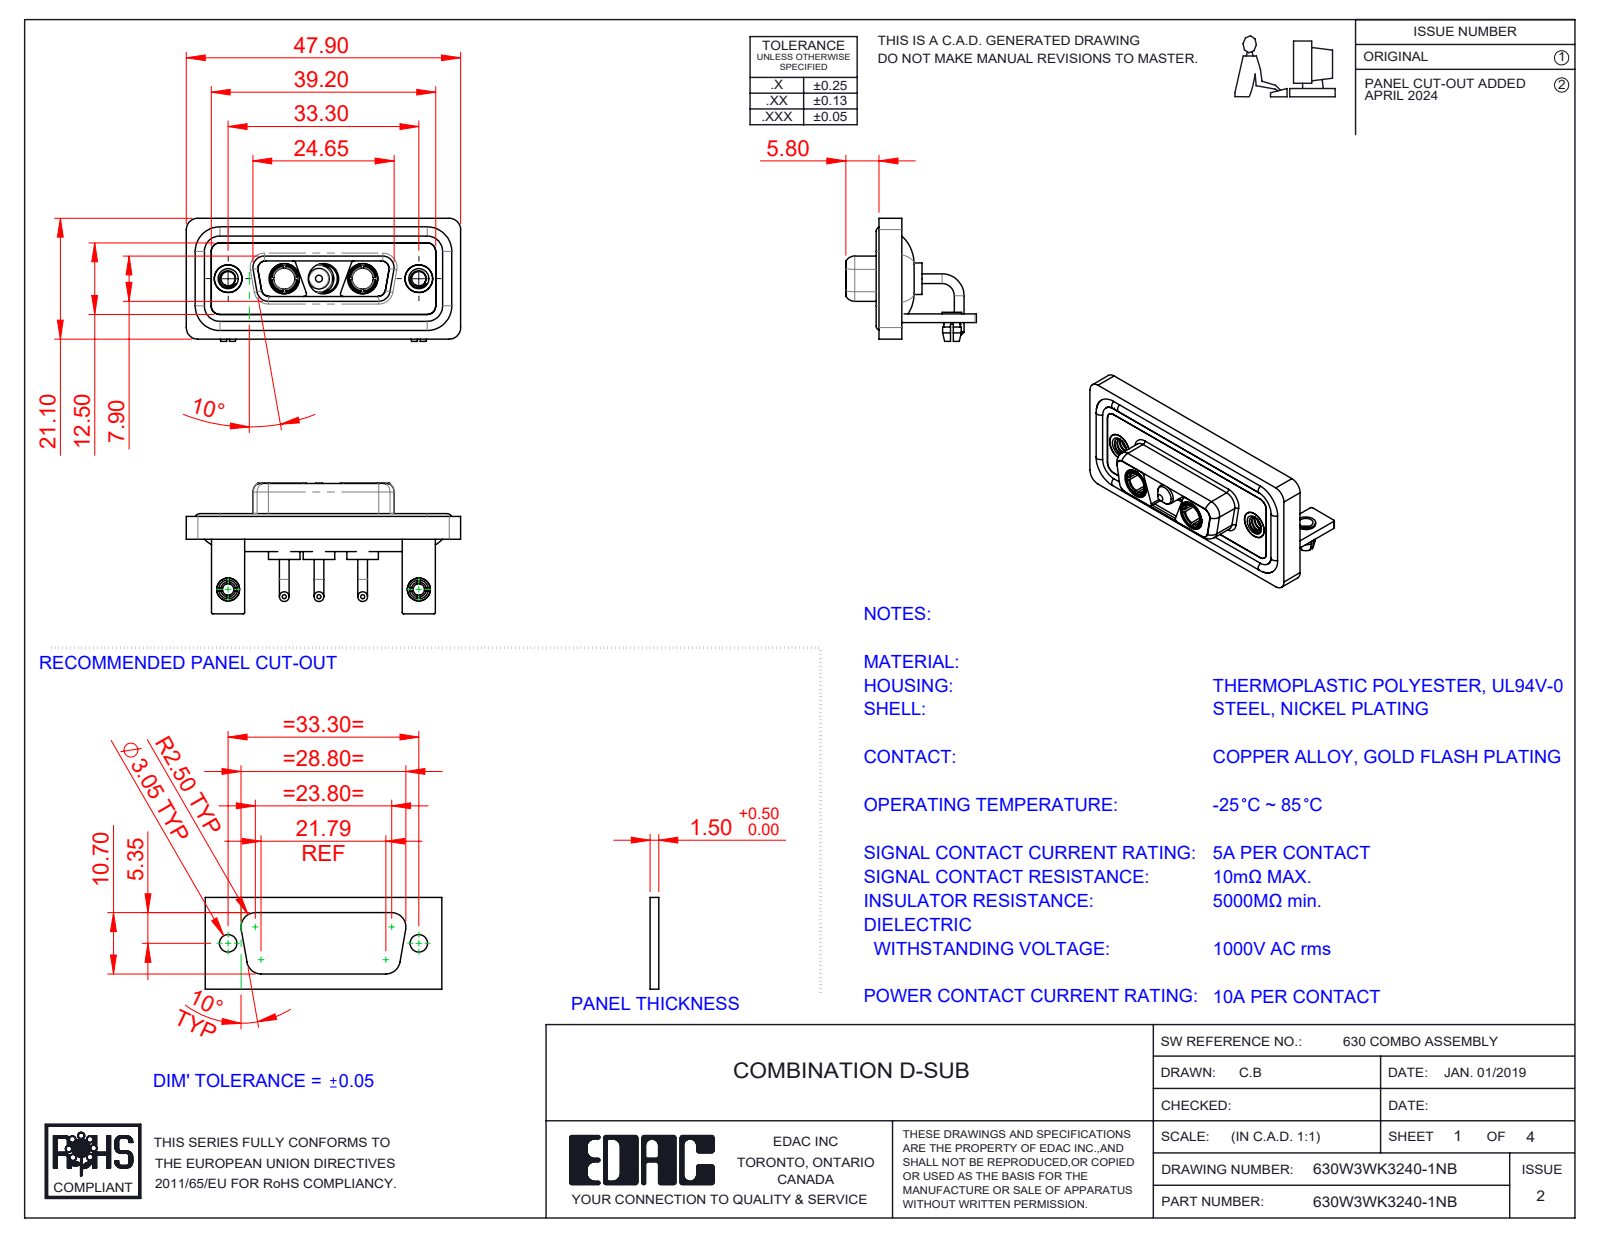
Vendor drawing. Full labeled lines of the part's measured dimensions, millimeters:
Part name (STEP PRODUCT): Power Socket_10A RA; 630Combo Shell Rear_15 Contacts; 630Combo Board Lock_50 Contacts; Power Pin_10A RA (+6 more)
STEP written by: SolidWorks 2023 (CONFIG_CONTROL_DESIGN)
Units: millimetres
Bodies: 17 solids, 729 faces (246 planar, 318 cylindrical, 165 other)
Overall size (bounding box): 47.9 × 22.8 × 21.5
Volume: 6 254 mm³ · Surface area: 10 535 mm²
Round holes (diameter × count): ⌀4.85 ×5, ⌀2.5 ×4, ⌀5.3 ×3, ⌀2 ×2, ⌀3.2 ×2, ⌀3.7 ×2, ⌀4 ×2, ⌀4.05 ×2, ⌀5 ×2
Round bosses / shafts (diameter × count): ⌀1.7 ×6, ⌀1.6 ×4, ⌀5.5 ×3, ⌀5.2 ×3, ⌀4.75 ×3, ⌀3.75 ×3, ⌀4.96 ×2, ⌀4.95 ×2
Partial cylindrical surfaces — rounded edges, fillets, slot ends (radius × count): R2 ×21, R1.5 ×18, R0.25 ×16, R1.35 ×12, R0.5 ×9, R1.6 ×8, R0.6 ×4, R0.65 ×4
Main face-to-face distances: 0.4, 2.9, 1.5, 3.7, 1.8, 1.1, 4.1, 1.6, 2.5, 1.4
Hole centre spacings: 6.85, 9.8, 16.65, 23.5, 33.3, 13.7
